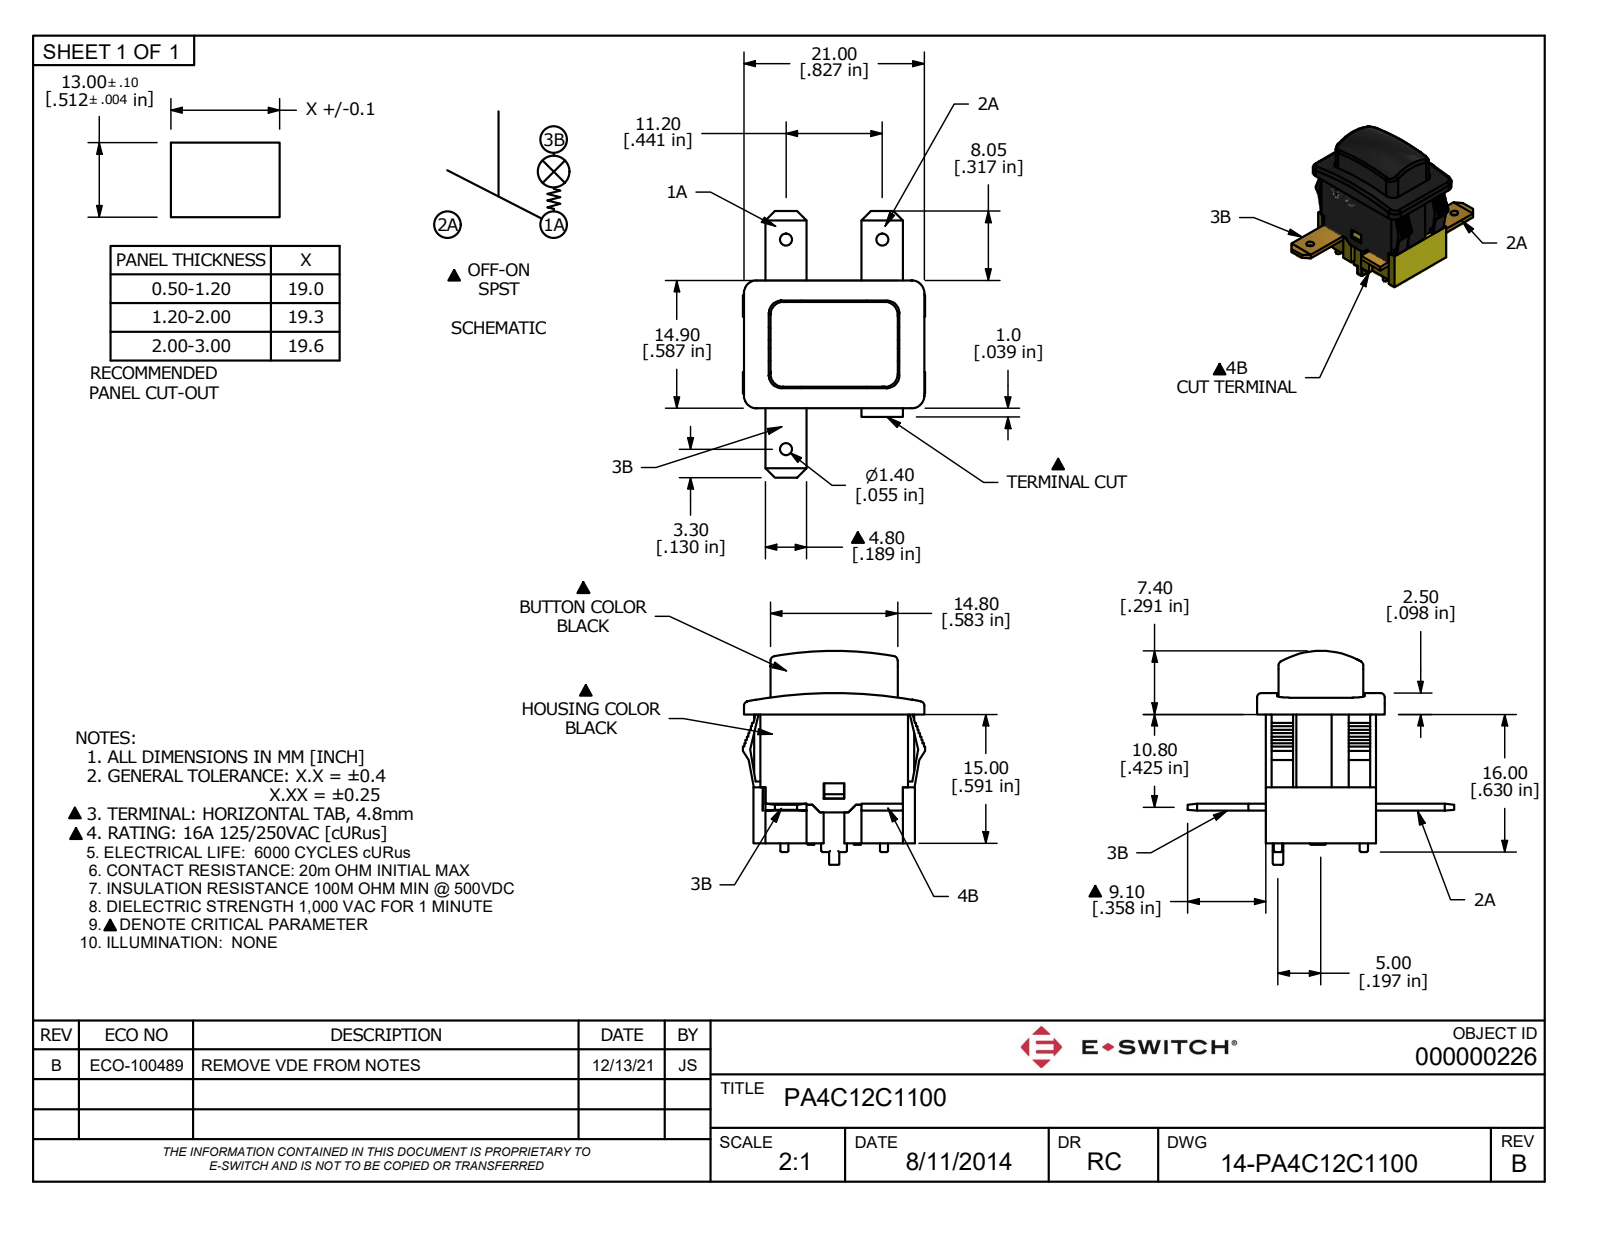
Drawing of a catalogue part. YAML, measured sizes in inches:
step_written_by: "Autodesk Inventor 2022 (AUTOMOTIVE_DESIGN)"
units: inches
bodies: {solids: 1, faces: 1222, planar: 924, cylindrical: 100, other: 198}
overall_size: [1.22, 0.98, 0.835]
volume: 0.155
surface_area: 9.164
round_holes:
  - {diameter: 0.055, count: 3}
  - {diameter: 0.039, count: 2}
  - {diameter: 0.118, count: 1}
round_bosses_or_shafts:
  - {diameter: 0.037, count: 4}
  - {diameter: 0.098, count: 2}
partial_cylinders:
  - {radius: 0.01, count: 21}
  - {radius: 0.005, count: 16}
  - {radius: 0.059, count: 12}
  - {radius: 0.006, count: 8}
  - {radius: 0.02, count: 5}
  - {radius: 0.031, count: 4}
  - {radius: 0.011, count: 3}
  - {radius: 0.039, count: 2}
face_to_face_distances: [0.031, 0.026, 0.035, 0.39, 0.024, 0.043, 0.447, 0.045, 0.415, 0.02]
hole_center_spacings: [0.528, 0.148, 0.483, 0.673, 0.228, 0.387, 0.441, 0.608]
